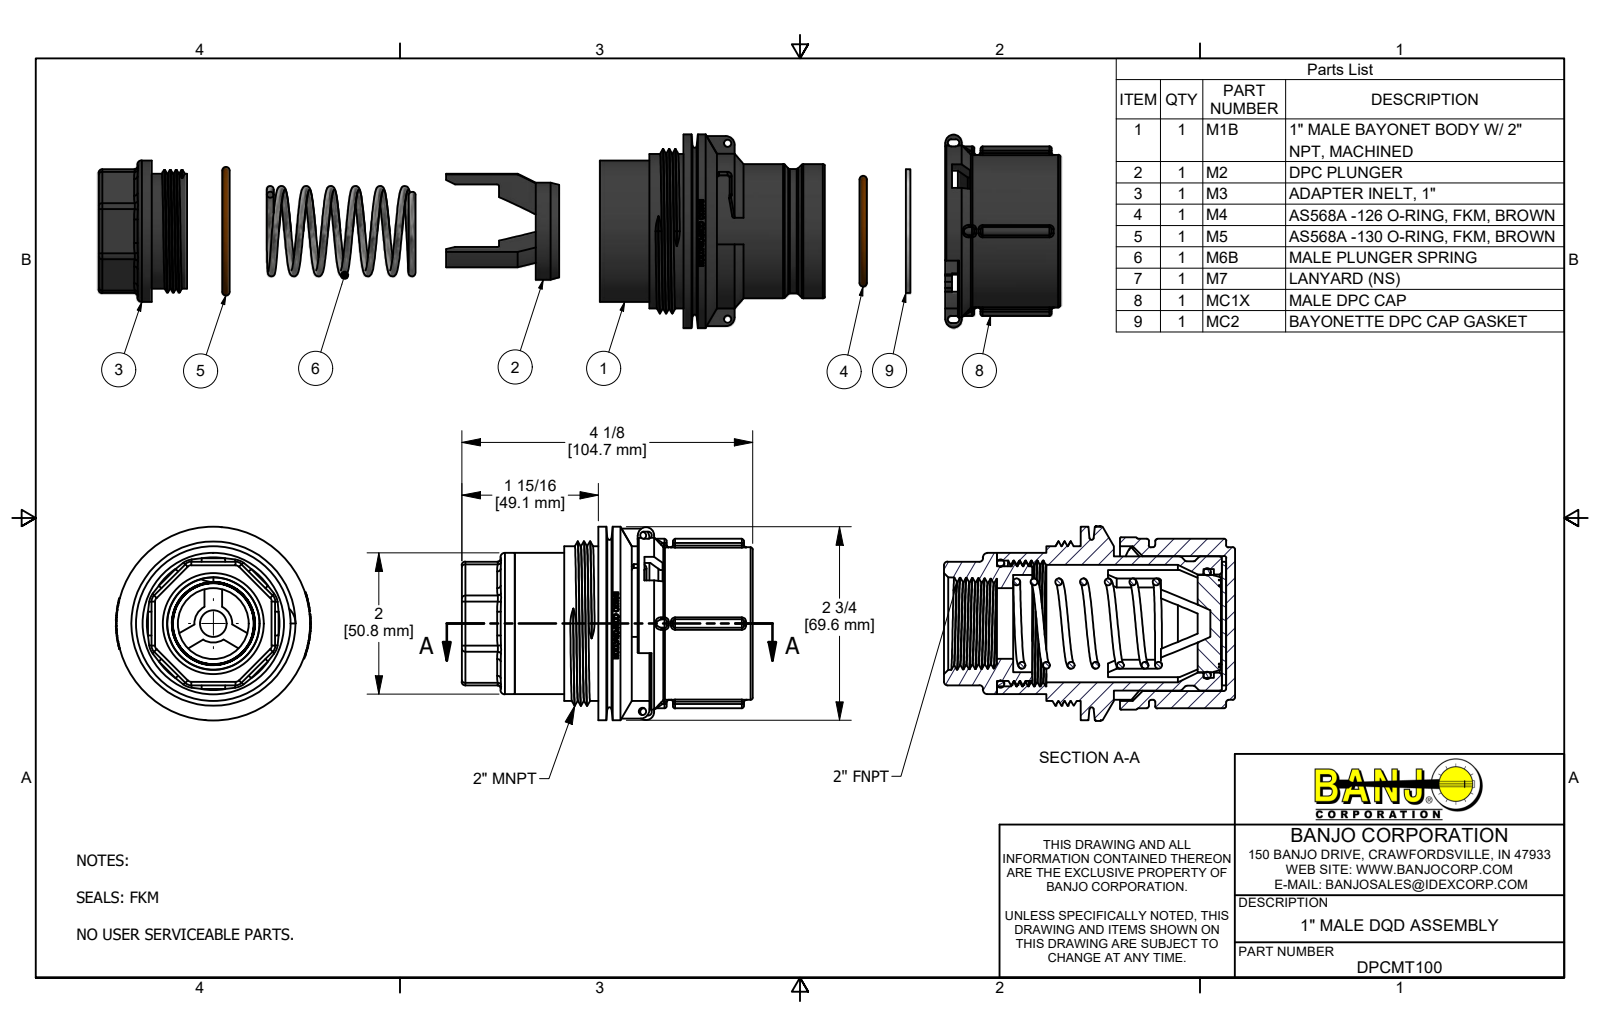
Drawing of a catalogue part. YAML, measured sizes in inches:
part_name: "DPCMT100; M1B; M1BY; M1BX (+8 more)"
step_written_by: "Autodesk Inventor 2019 (AUTOMOTIVE_DESIGN)"
units: inches
bodies: {solids: 11, faces: 1376, planar: 581, cylindrical: 212, other: 583}
overall_size: [21.137, 8.781, 3]
volume: 9.11
surface_area: 217.5
round_holes:
  - {diameter: 0.1, count: 2}
  - {diameter: 1.125, count: 1}
  - {diameter: 1.375, count: 1}
  - {diameter: 1.39, count: 1}
  - {diameter: 1.54, count: 1}
  - {diameter: 1.663, count: 1}
  - {diameter: 1.67, count: 1}
  - {diameter: 1.78, count: 1}
  - {diameter: 1.91, count: 1}
  - {diameter: 2.19, count: 1}
  - {diameter: 2.2, count: 1}
  - {diameter: 2.57, count: 1}
round_bosses_or_shafts:
  - {diameter: 3, count: 1}
  - {diameter: 2.74, count: 1}
  - {diameter: 2.563, count: 1}
  - {diameter: 2.44, count: 1}
  - {diameter: 2.327, count: 1}
  - {diameter: 2.188, count: 1}
  - {diameter: 2.16, count: 1}
  - {diameter: 2, count: 1}
partial_cylinders:
  - {radius: 0.03, count: 32}
  - {radius: 0.05, count: 20}
  - {radius: 0.06, count: 8}
  - {radius: 0.12, count: 8}
  - {radius: 0.116, count: 2}
  - {radius: 0.125, count: 2}
  - {radius: 0.291, count: 1}
  - {radius: 0.391, count: 1}
face_to_face_distances: [1.876, 0.03, 1.846, 0.125, 1.814, 1.784, 0.062, 2.001, 1.971, 0.187]
hole_center_spacings: [2.49, 6]
